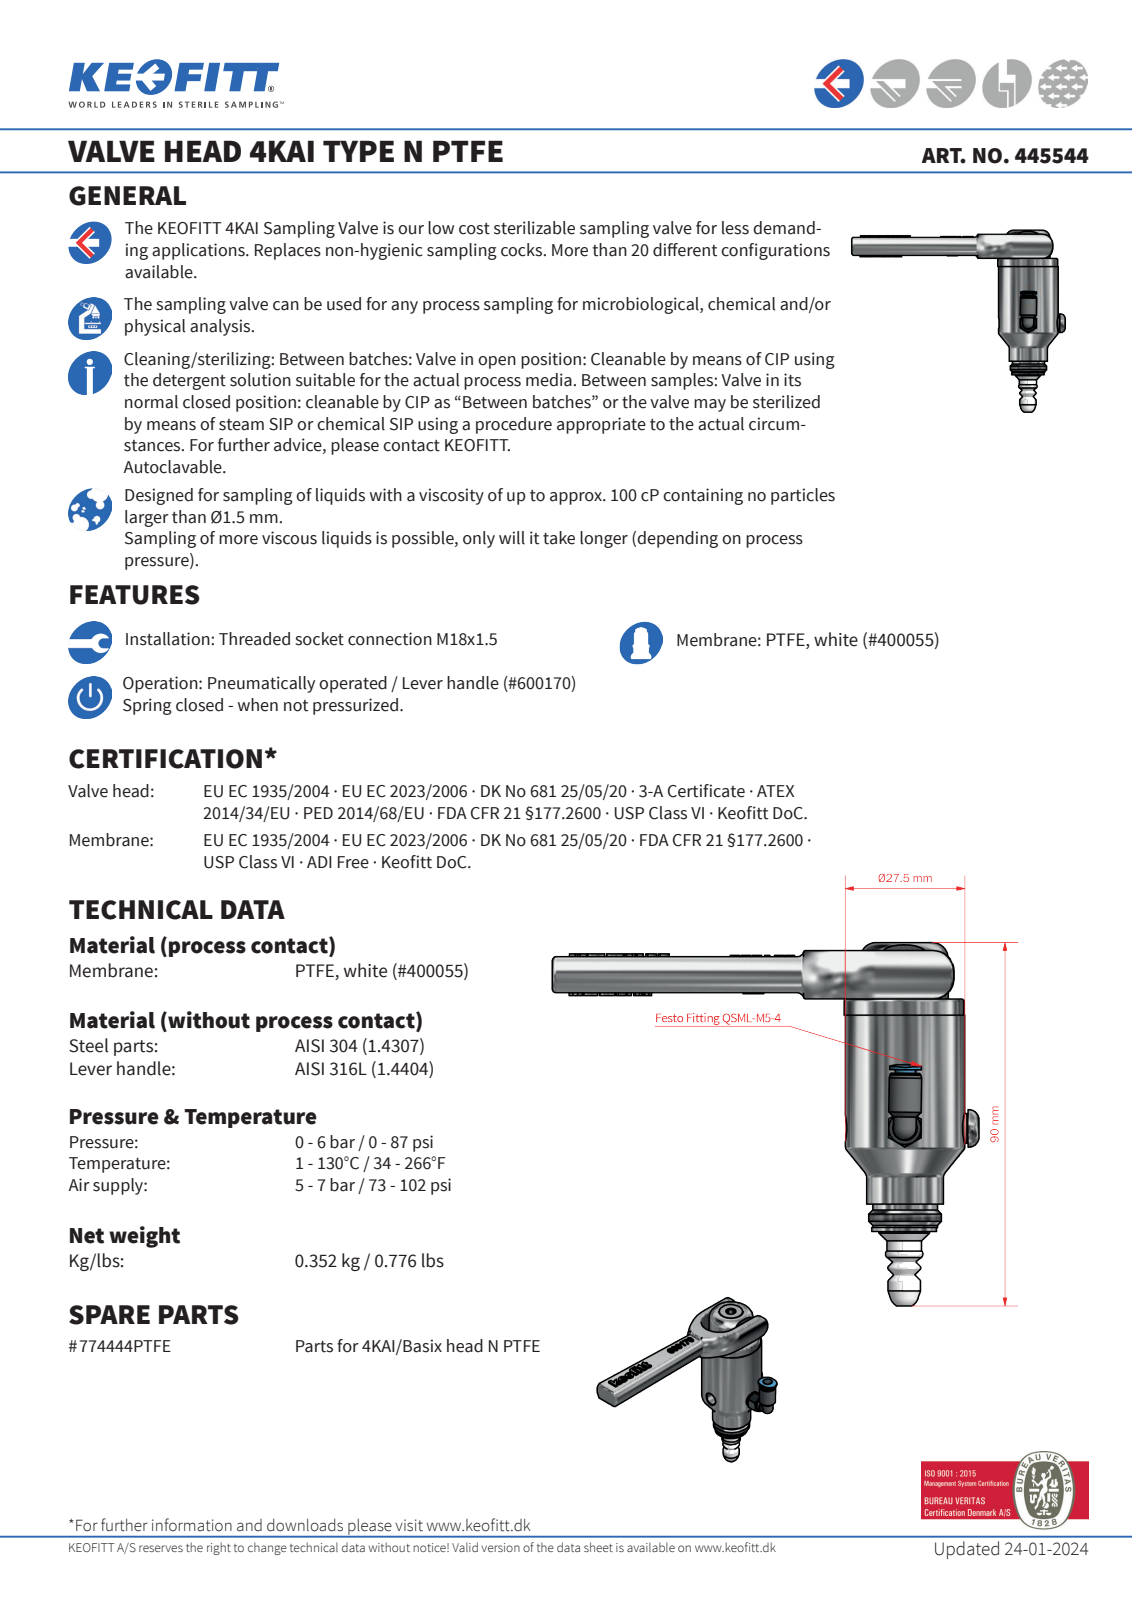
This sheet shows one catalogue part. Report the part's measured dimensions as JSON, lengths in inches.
{"part_name": "445544", "step_written_by": "Autodesk Inventor 2020 (AUTOMOTIVE_DESIGN)", "units": "inches", "bodies": {"solids": 1, "faces": 740, "planar": 295, "cylindrical": 121, "other": 324}, "overall_size": [4.145, 3.541, 1.769], "volume_in3": 2.865, "surface_area_in2": 31.77, "round_holes": [[0.199, 3], [0.067, 2], [0.118, 2], [0.169, 2], [0.315, 2], [0.157, 1], [0.183, 1], [0.238, 1], [0.24, 1], [0.274, 1], [0.472, 1], [0.512, 1]], "round_bosses_or_shafts": [[0.197, 4], [1.161, 2], [0.63, 2], [0.291, 2], [0.26, 2], [0.236, 2], [0.22, 2], [0.768, 1]], "partial_cylinders_radius": [[0.02, 14], [0.02, 12], [0.039, 2], [0.059, 2], [0.118, 2], [0.154, 2], [0.197, 2], [0.276, 2]], "face_to_face_distances": [0.059, 0.413, 0.354, 0.472, 0.079, 1.378, 2.677, 0.157, 1.22, 1.299], "hole_center_spacings": [0.394, 0.015, 0.385, 0.392, 0.395, 0.404, 0.787]}
